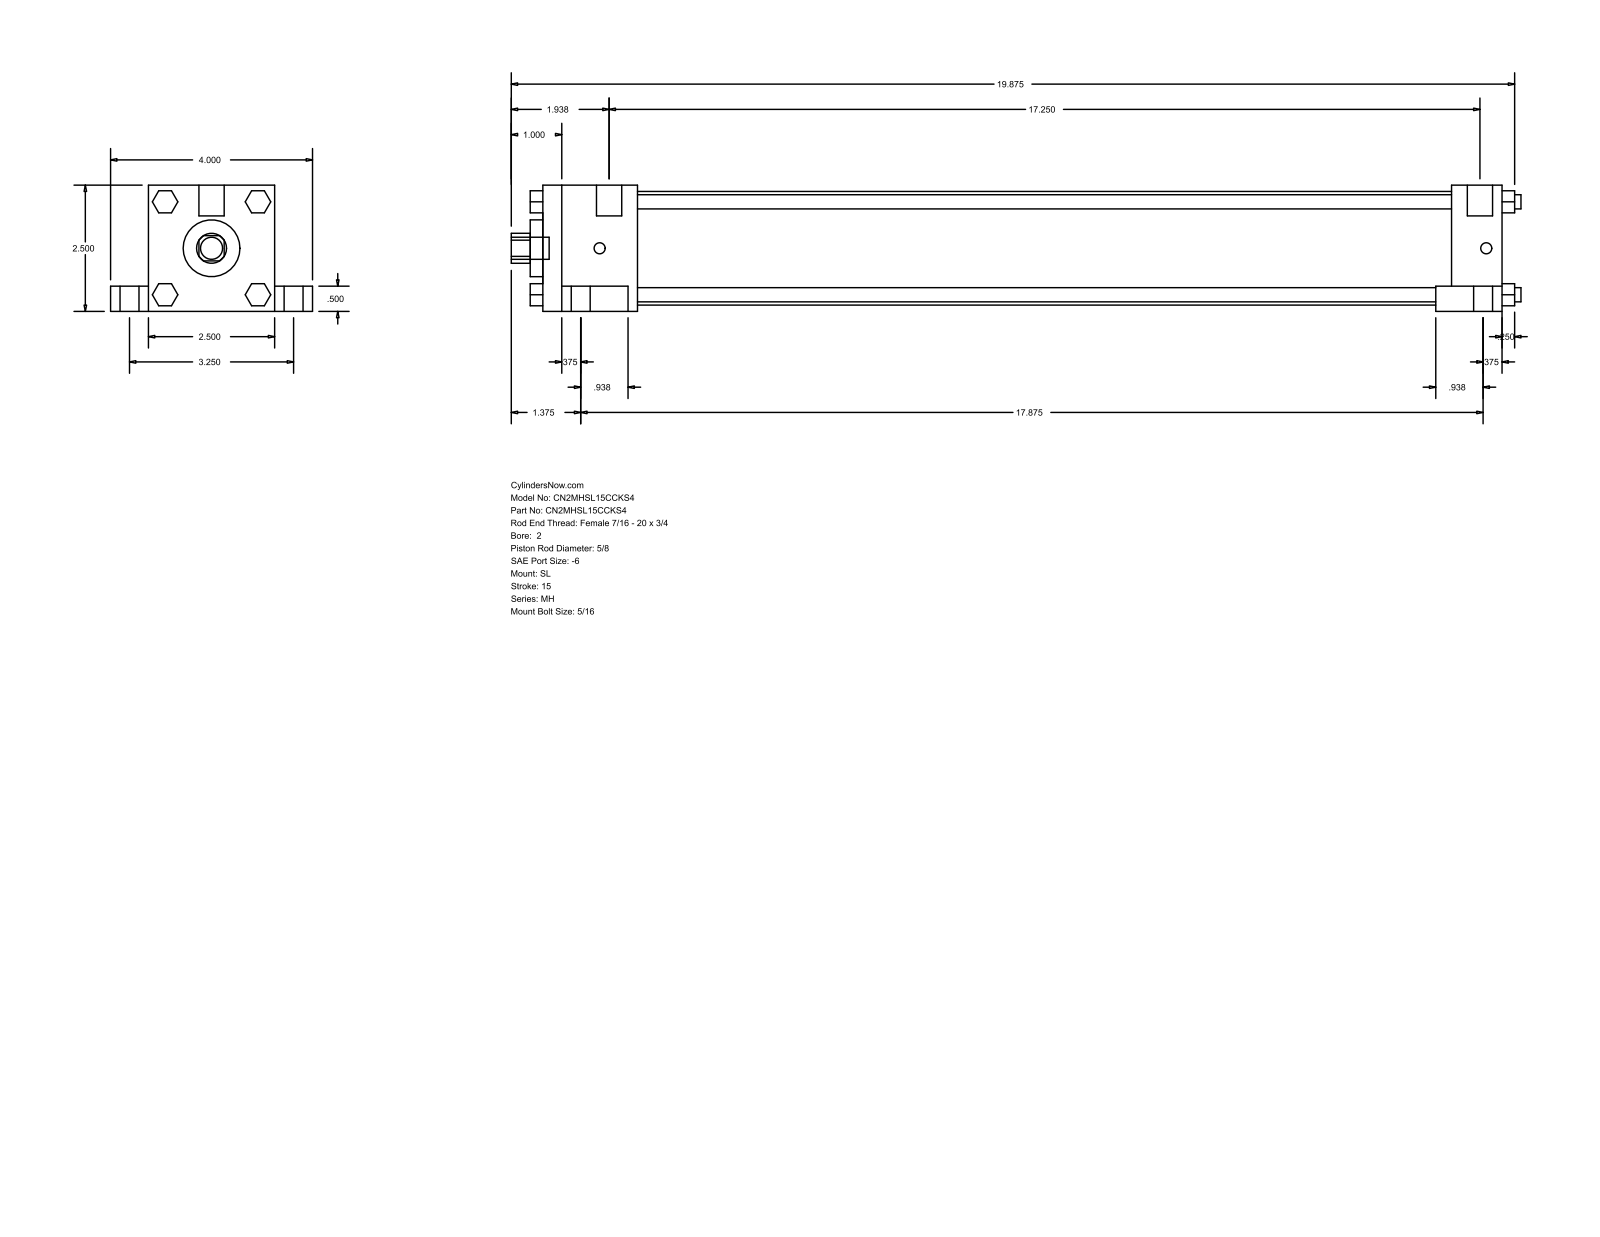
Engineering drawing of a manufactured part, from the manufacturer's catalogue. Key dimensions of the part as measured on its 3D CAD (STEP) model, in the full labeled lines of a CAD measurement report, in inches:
Part name (STEP PRODUCT): MH_SL__0200_0.625
STEP written by: GSSL Pune (CONFIG_CONTROL_DESIGN)
Units: inches
Bodies: 0 solids, 148 faces (112 planar, 36 cylindrical, 0 other)
Overall size (bounding box): 20 × 4 × 2.5
Round holes (diameter × count): ⌀0.625 ×1, ⌀1.125 ×1, ⌀2.25 ×1
Round bosses / shafts (diameter × count): ⌀0.625 ×4, ⌀0.375 ×4, ⌀0.281 ×4, ⌀0.219 ×4, ⌀0.5 ×2, ⌀0.437 ×1
Partial cylindrical surfaces — rounded edges, fillets, slot ends (radius × count): R0.297 ×1
Main face-to-face distances: 2.5, 19, 0.5, 0.75, 2, 3.25, 18, 1, 1.875, 16.125
